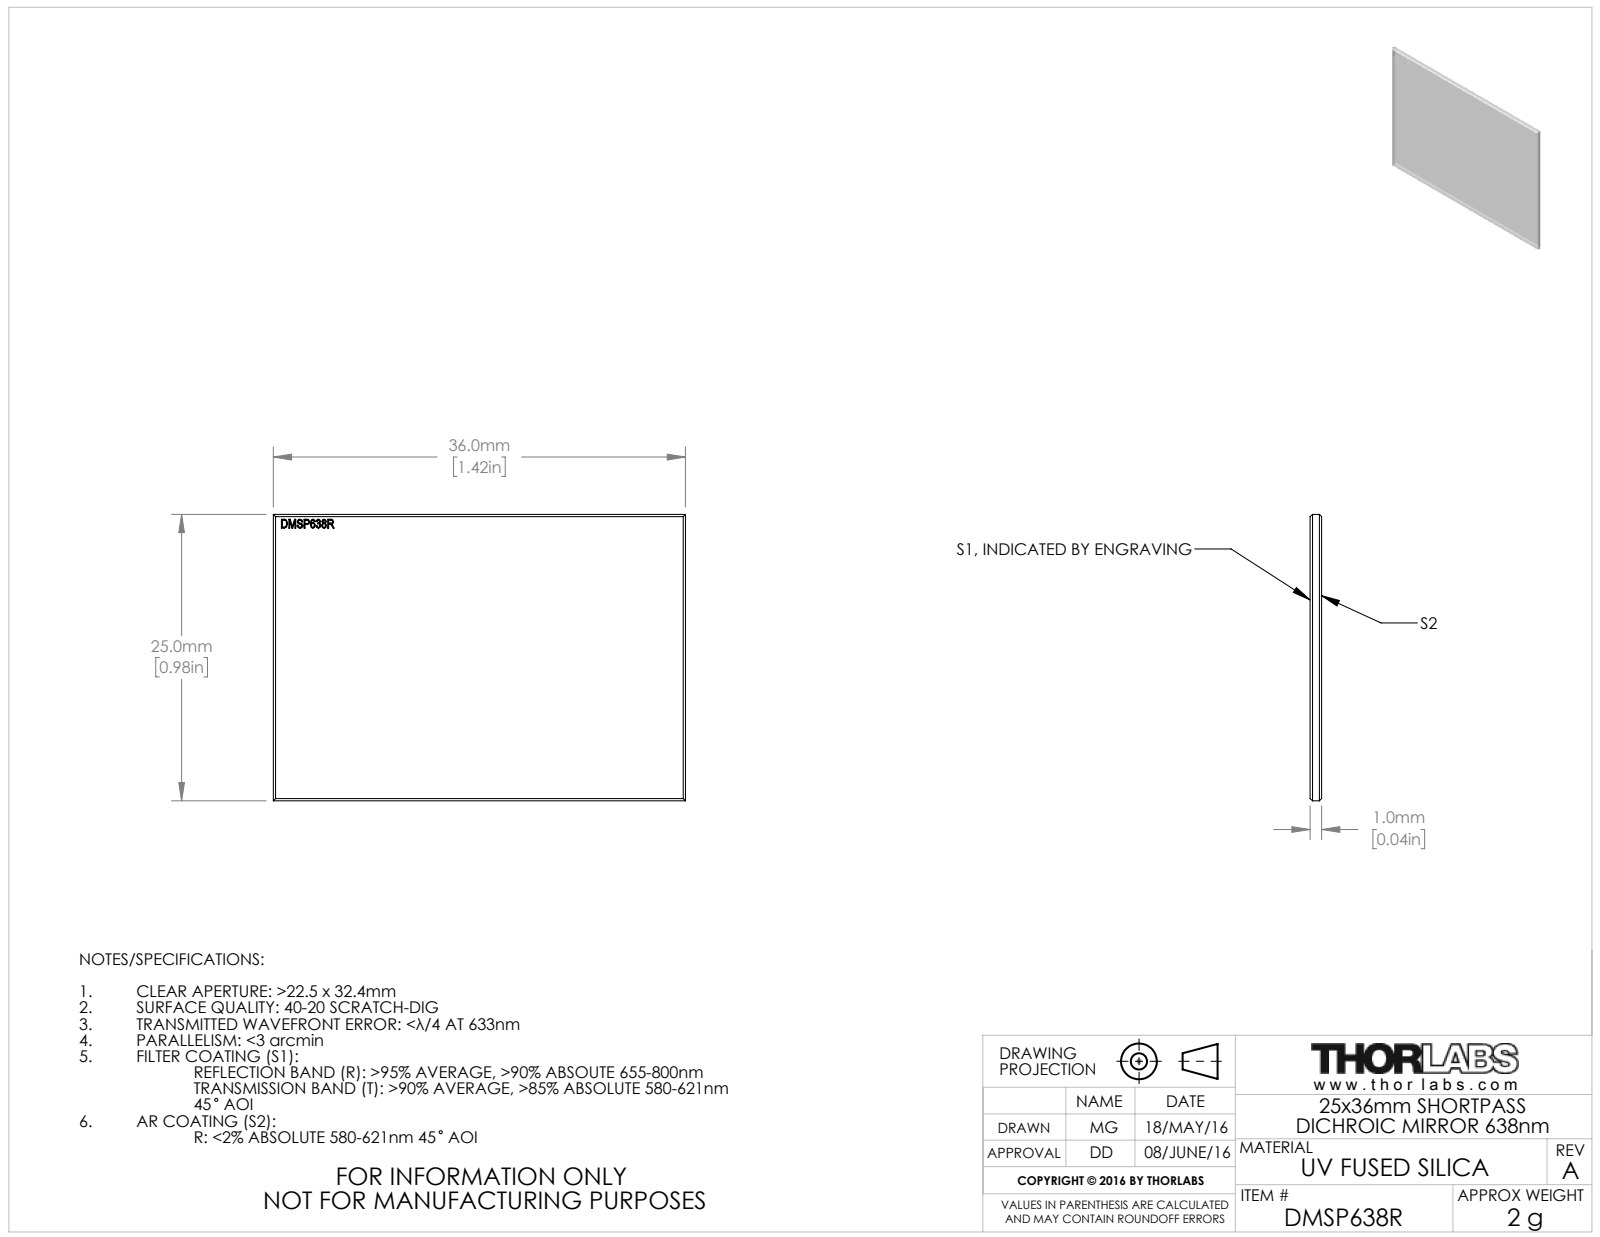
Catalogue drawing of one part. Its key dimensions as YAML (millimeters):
part_name: "TTN045182-E0W"
step_written_by: "SolidWorks 2016 (CONFIG_CONTROL_DESIGN)"
units: millimeters
bodies: {solids: 1, faces: 151, planar: 74, cylindrical: 0, other: 77}
overall_size: [36, 25, 1]
volume: 895
surface_area: 1894
face_to_face_distances: [1, 25, 18.1, 36, 25.88, 0.99, 0.72, 1.97, 0.8, 1.25]
